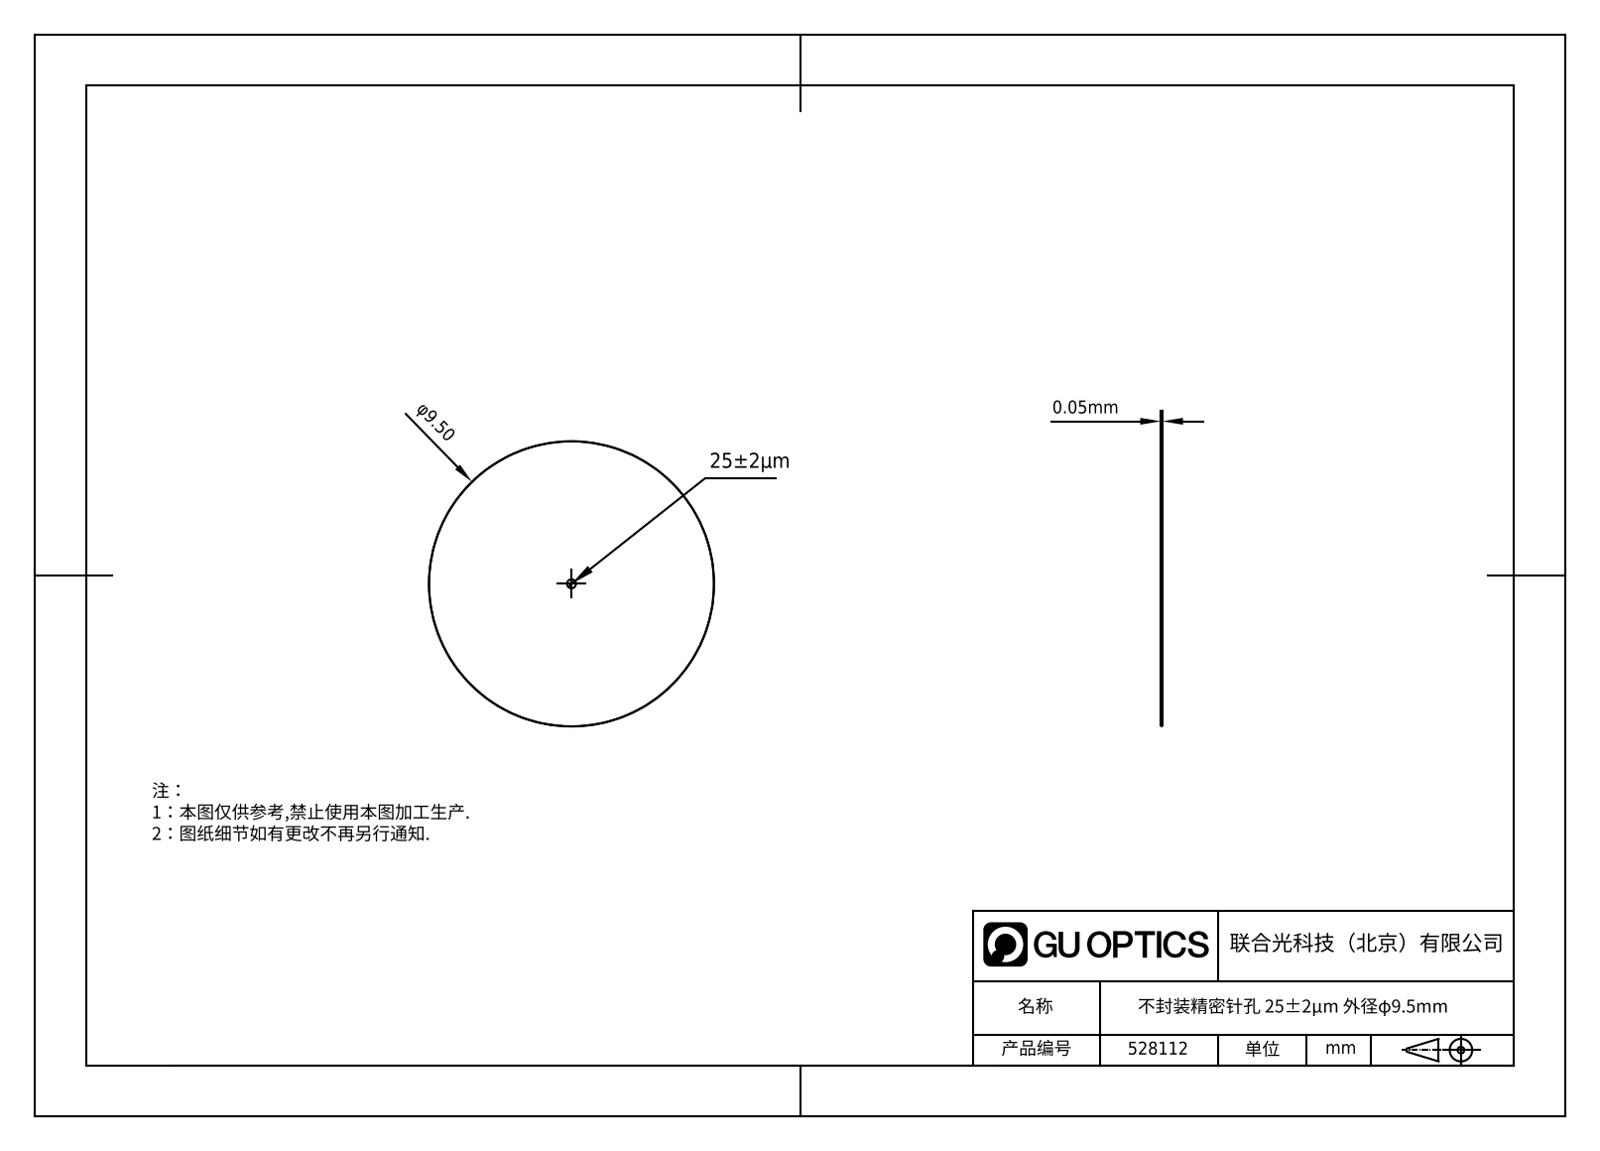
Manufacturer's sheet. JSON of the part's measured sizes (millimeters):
{"part_name": "1.5.3.5-ZXO-9.5-25", "step_written_by": "SolidWorks 2021 (CONFIG_CONTROL_DESIGN)", "units": "millimeters", "bodies": {"solids": 1, "faces": 6, "planar": 2, "cylindrical": 4, "other": 0}, "overall_size": [9.5, 9.5, 0.05], "volume_mm3": 4, "surface_area_mm2": 143, "round_bosses_or_shafts": [[9.5, 1]]}
